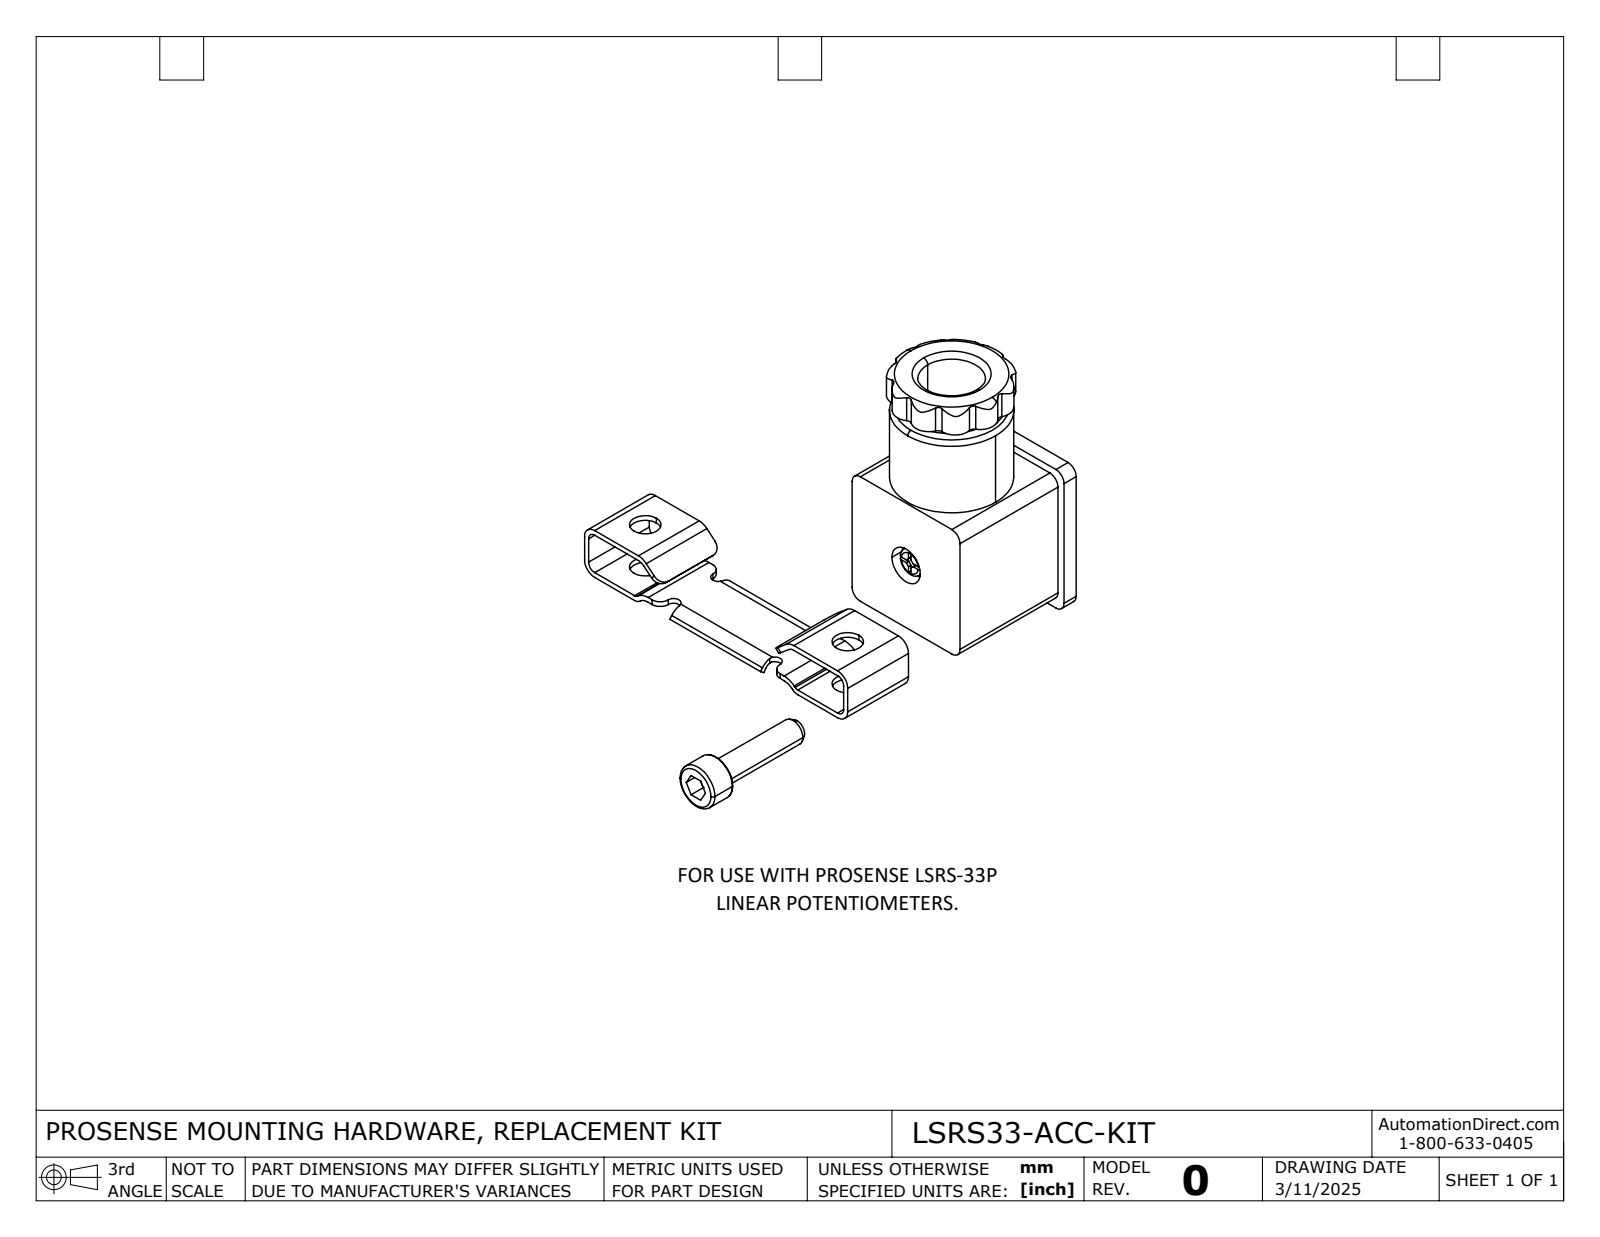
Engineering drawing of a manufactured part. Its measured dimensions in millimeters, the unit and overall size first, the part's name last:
Units: millimetres
Overall size (bounding box): 94.5 × 66.7 × 50.3
Round holes (diameter × count): ⌀5.5 ×2, ⌀2.8 ×1, ⌀5.3 ×1, ⌀7 ×1, ⌀10 ×1, ⌀11.8 ×1, ⌀15.3 ×1, ⌀22 ×1
Round bosses / shafts (diameter × count): ⌀21.7 ×1, ⌀17 ×1, ⌀8.4 ×1, ⌀6.3 ×1, ⌀5.4 ×1, ⌀4.9 ×1, ⌀2.6 ×1
Partial cylindrical surfaces — rounded edges, fillets, slot ends (radius × count): R2 ×20, R1 ×13, R3.1 ×11, R0.5 ×8, R1.5 ×6, R3 ×6, R1.3 ×4, R2.5 ×4
Main face-to-face distances: 1.6, 25, 1, 23.4, 1.8, 26.6, 23.2, 24.8, 24, 2
Hole centre spacings: 31.98, 50, 54.25
Volume: 18 938 mm³ · Surface area: 20 027 mm²
Bodies: 6 solids, 395 faces (166 planar, 202 cylindrical, 27 other)
Part name (STEP PRODUCT): LSRS33-ACC-KIT
STEP written by: SolidWorks 2024 (AUTOMOTIVE_DESIGN)
